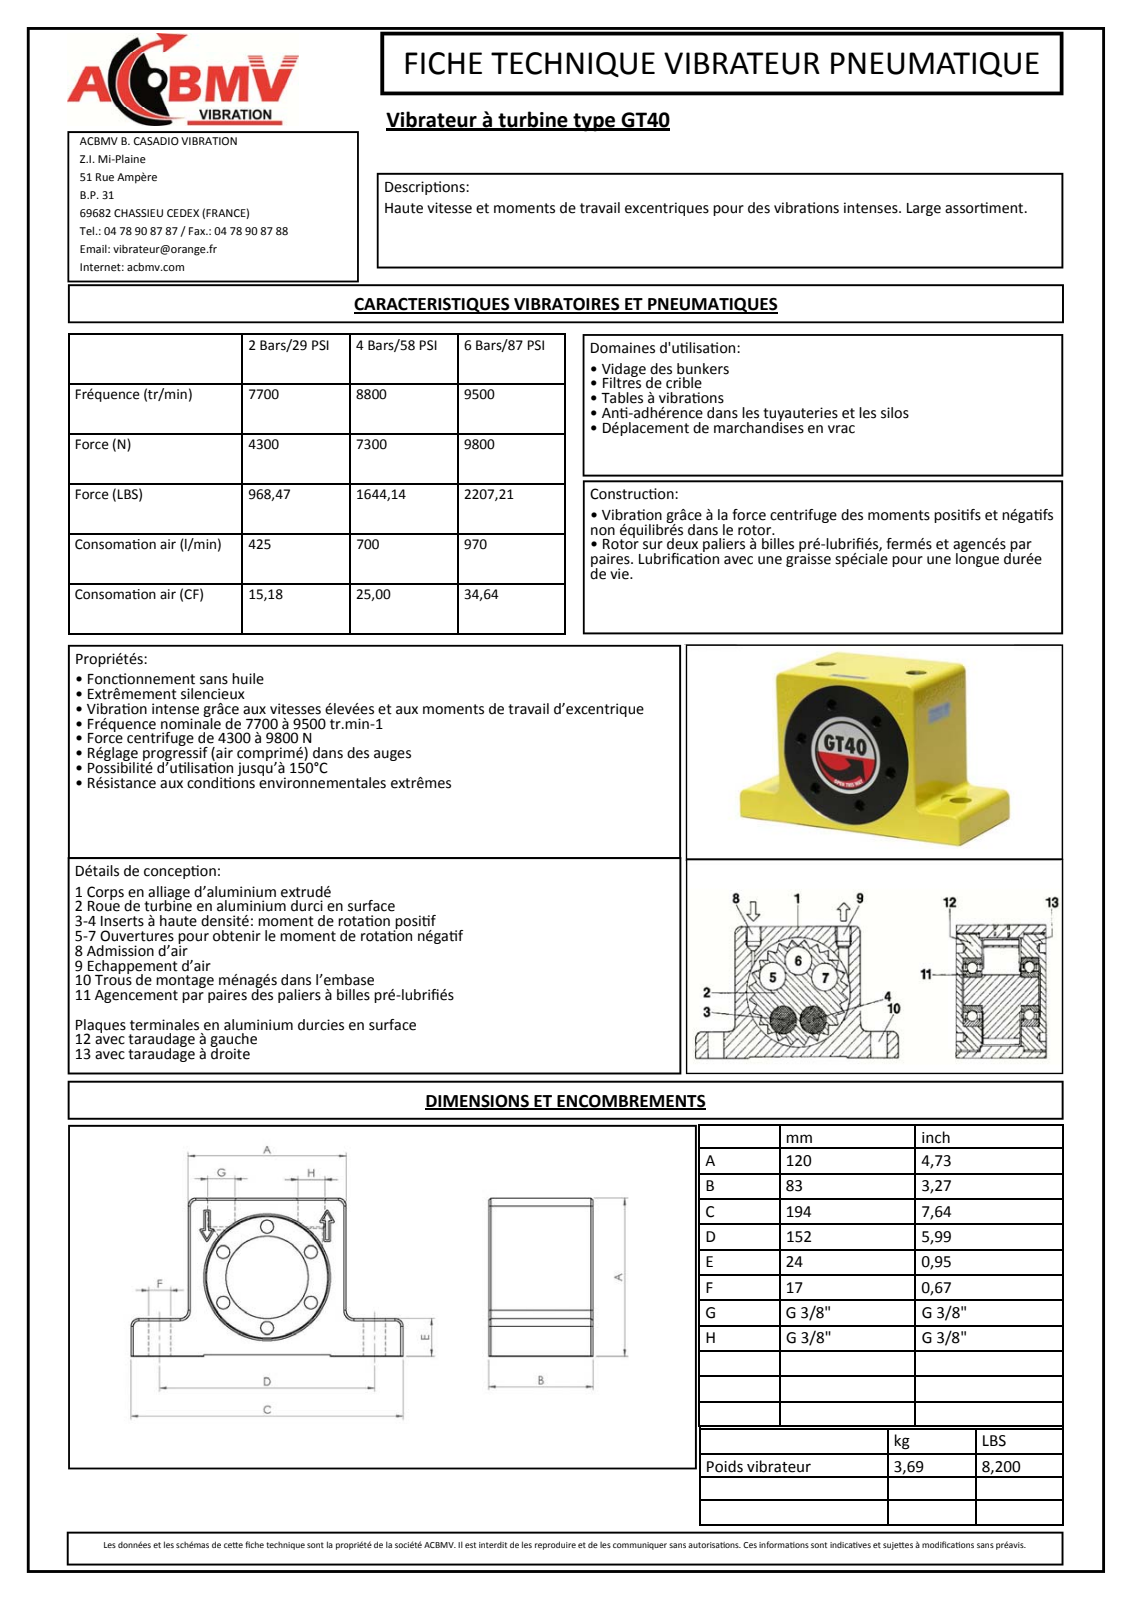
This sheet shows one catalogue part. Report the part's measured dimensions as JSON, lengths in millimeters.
{"part_name": "8040-00-M", "step_written_by": "Autodesk Inventor 2011 (CONFIG_CONTROL_DESIGN)", "units": "millimeters", "bodies": {"solids": 1, "faces": 287, "planar": 180, "cylindrical": 76, "other": 31}, "overall_size": [194, 120, 86], "volume_mm3": 1350000, "surface_area_mm2": 103508, "round_holes": [[8.5, 6], [14.95, 2], [17, 2], [30, 2], [3.94, 1], [52, 1], [61, 1], [62, 1]], "round_bosses_or_shafts": [[3.54, 1]], "partial_cylinders_radius": [[0.3, 14], [5, 6], [1.02, 4], [0.68, 3], [1.19, 3], [1.36, 3], [2.72, 3], [0.51, 2]], "face_to_face_distances": [120, 0.8, 85.7, 119.2, 6.7, 7, 79, 78.7, 86, 6.65], "hole_center_spacings": [40, 69.28, 80, 36, 116, 28.39, 52.98, 75.1]}
